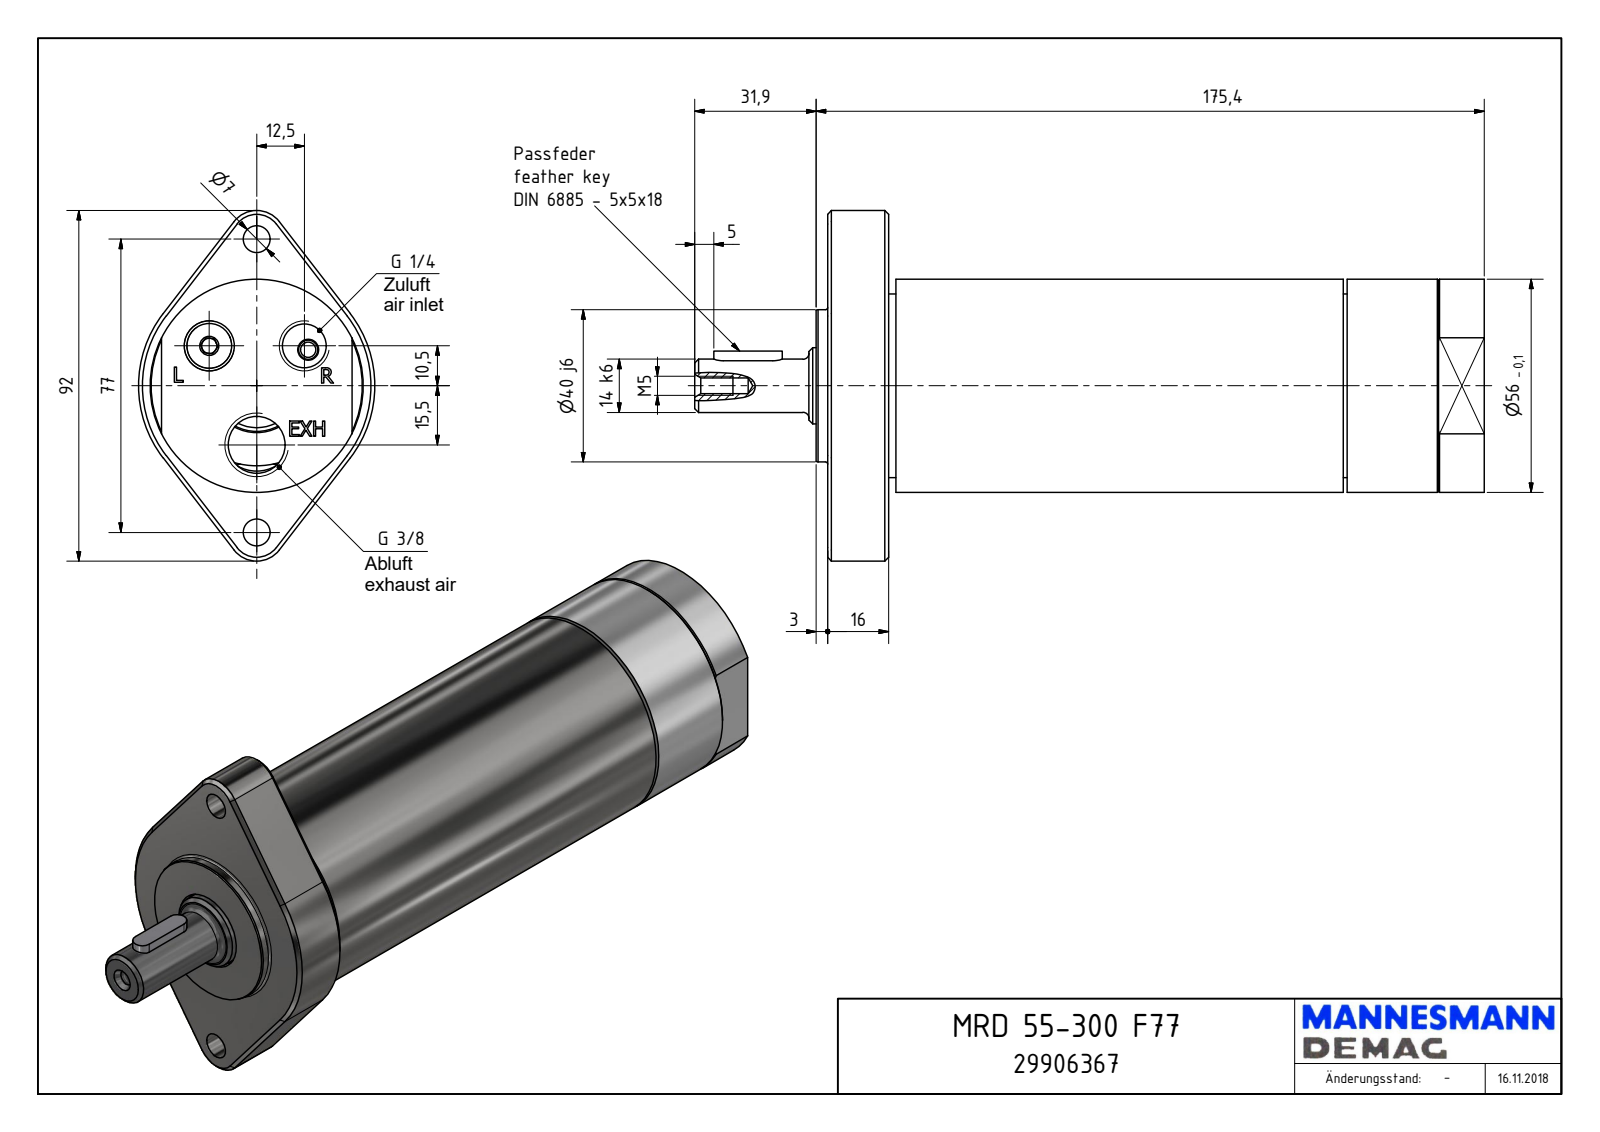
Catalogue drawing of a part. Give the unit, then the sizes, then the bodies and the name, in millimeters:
Units: millimetres
Overall size (bounding box): 207.3 × 92 × 62
Round holes (diameter × count): ⌀7 ×2, ⌀4 ×1, ⌀4.13 ×1, ⌀11.45 ×1, ⌀14.95 ×1, ⌀21 ×1, ⌀21.25 ×1, ⌀23.54 ×1, ⌀26 ×1, ⌀48.38 ×1
Round bosses / shafts (diameter × count): ⌀56 ×1, ⌀48.18 ×1, ⌀40 ×1, ⌀19.95 ×1, ⌀14 ×1
Partial cylindrical surfaces — rounded edges, fillets, slot ends (radius × count): R2.5 ×2, R6 ×2, R7.5 ×2, R5.72 ×1, R21.93 ×1, R23 ×1, R31 ×1
Main face-to-face distances: 172.4, 16, 156.4, 3, 19, 175.4, 1.9, 20.9, 17.9, 154.5
Hole centre spacings: 16.32, 28.85, 30.66, 38.5, 50.57, 15.5, 23, 25
Volume: 445 643 mm³ · Surface area: 47 096 mm²
Bodies: 1 solid, 208 faces (117 planar, 36 cylindrical, 55 other)
Part name (STEP PRODUCT): MRD 55-300 F77_29906367
STEP written by: Autodesk Inventor 2018 (AUTOMOTIVE_DESIGN)
